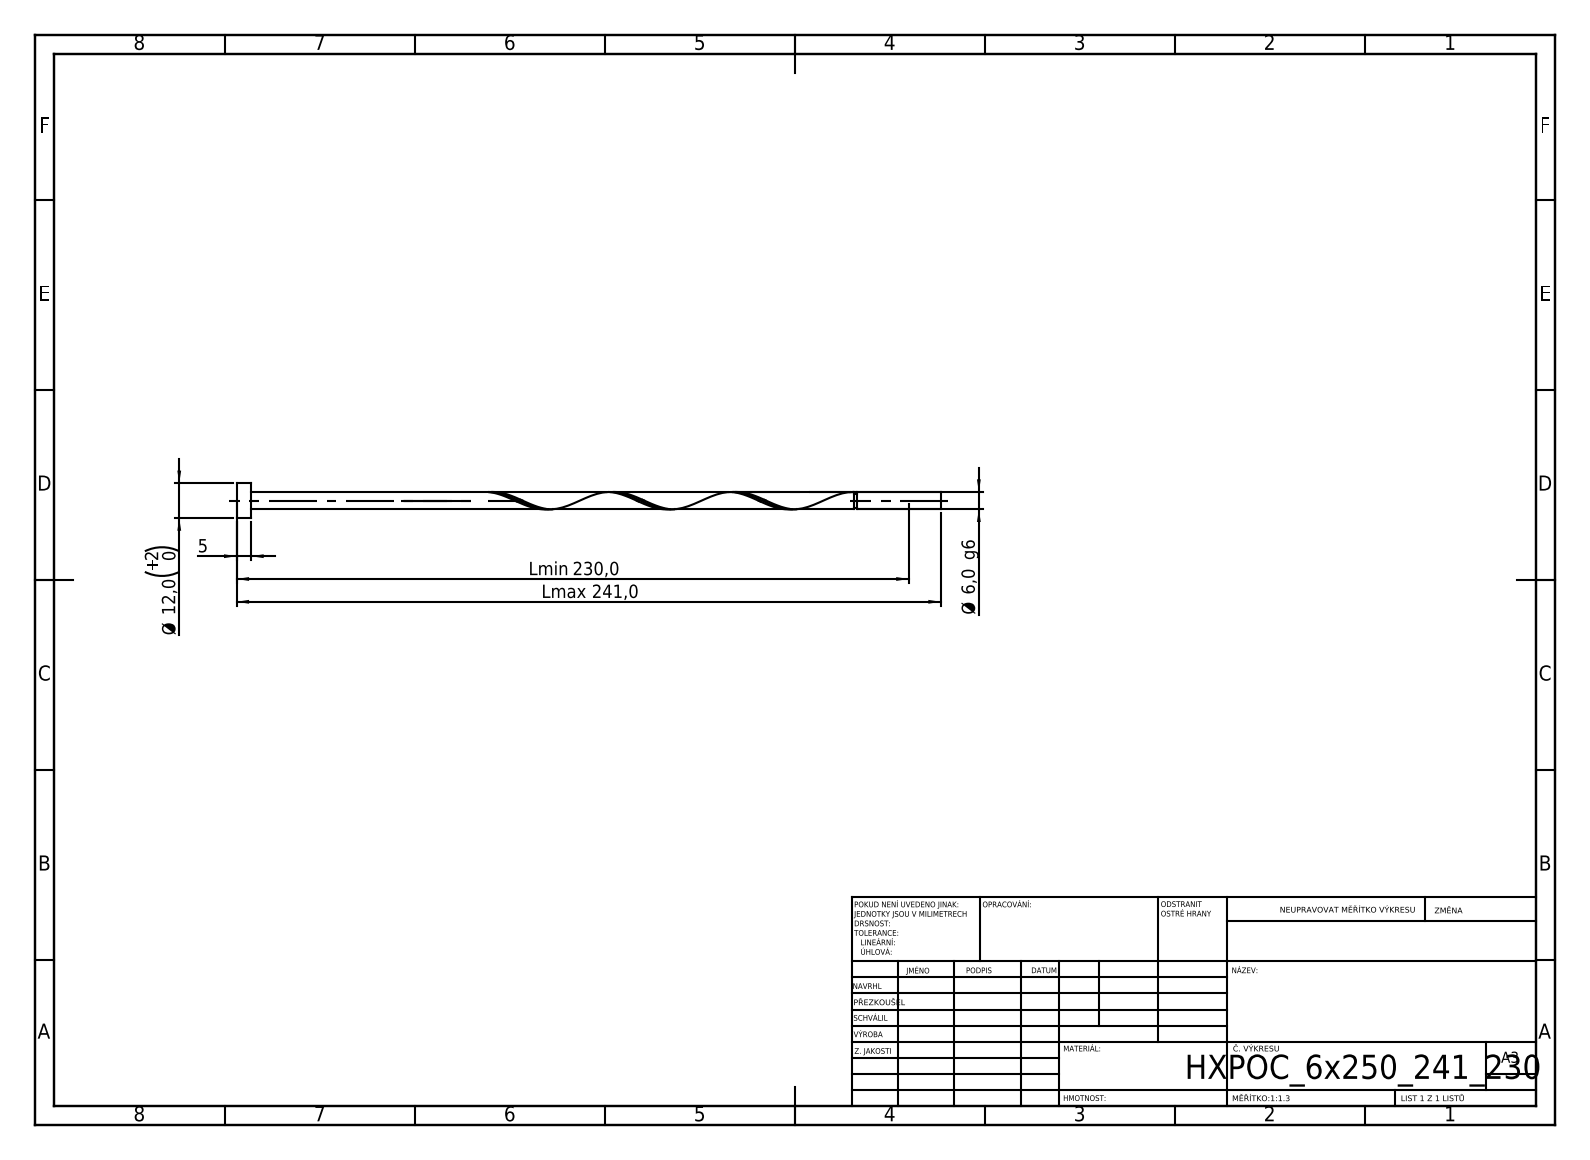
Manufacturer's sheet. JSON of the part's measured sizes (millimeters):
{"step_written_by": "SolidWorks 2019 (CONFIG_CONTROL_DESIGN)", "units": "millimeters", "bodies": {"solids": 1, "faces": 21, "planar": 6, "cylindrical": 14, "other": 1}, "overall_size": [241, 12, 12], "volume_mm3": 7158, "surface_area_mm2": 4960, "round_bosses_or_shafts": [[12, 1], [6, 1], [4.8, 1]], "face_to_face_distances": [5, 241, 236, 212.38, 207.38, 28.62, 211.18, 206.18, 1.2, 29.82]}
